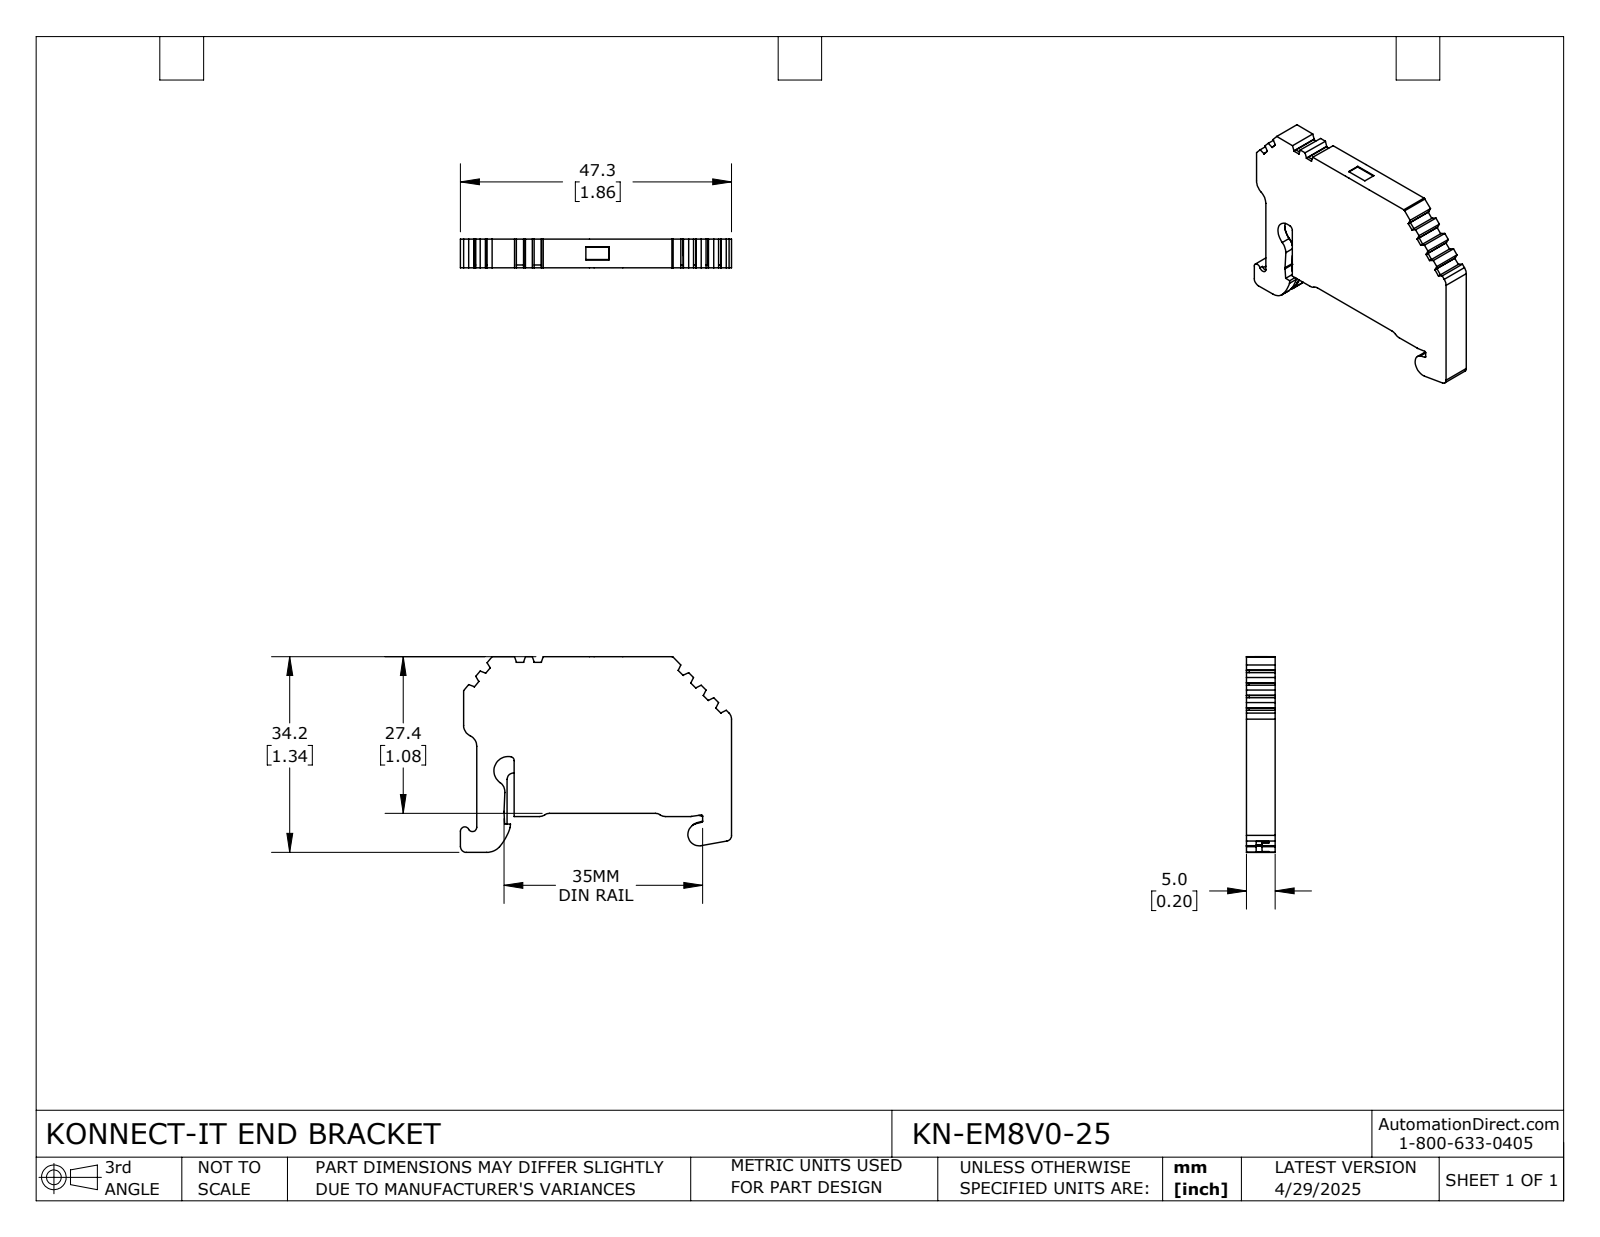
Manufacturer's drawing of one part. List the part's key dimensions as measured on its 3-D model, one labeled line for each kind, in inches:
Part name (STEP PRODUCT): KN-EM8V0-25
STEP written by: SolidWorks 2024 (CONFIG_CONTROL_DESIGN)
Units: inches
Bodies: 1 solid, 244 faces (156 planar, 87 cylindrical, 1 other)
Overall size (bounding box): 1.864 × 1.345 × 0.197
Volume: 0.375 in³ · Surface area: 5.499 in²
Partial cylindrical surfaces — rounded edges, fillets, slot ends (radius × count): R0.02 ×17, R0.059 ×5, R0.079 ×4, R0.008 ×3, R0.012 ×3, R0.039 ×3, R0.016 ×2, R0.03 ×2
Main face-to-face distances: 0.197, 1.077, 1.752, 0.022, 0.115, 0.258, 1.494, 1.098, 0.09, 0.348
